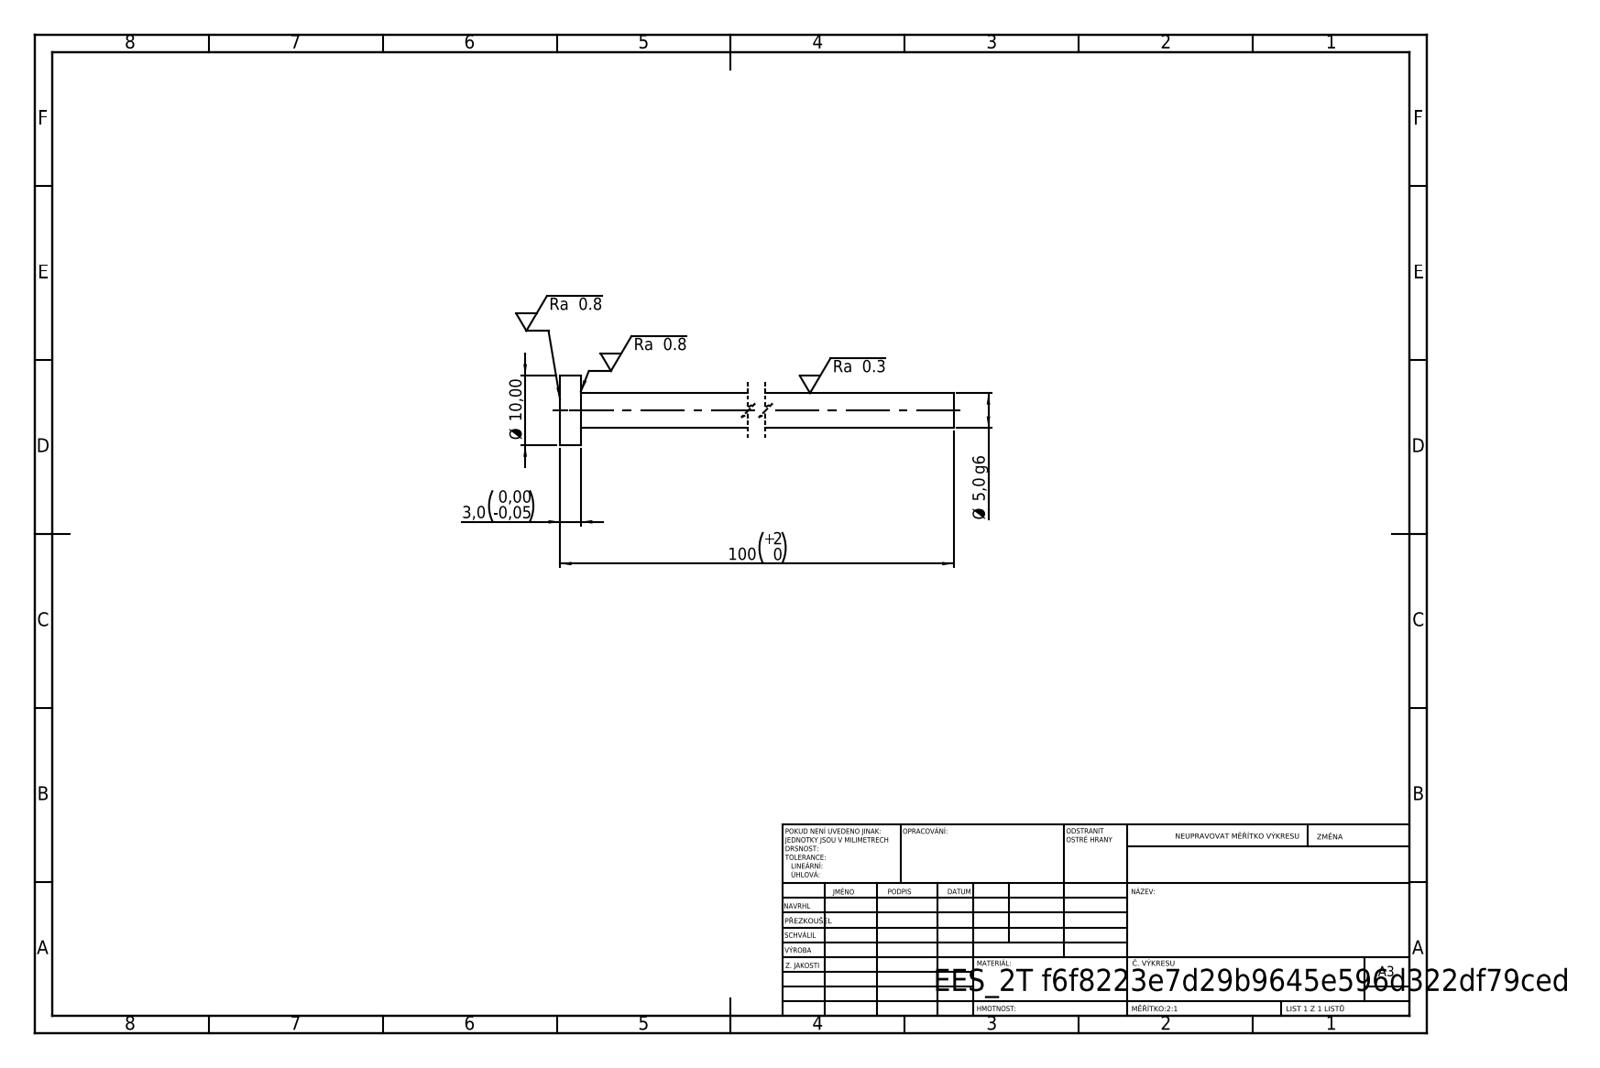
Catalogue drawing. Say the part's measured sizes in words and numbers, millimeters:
Its 3-D file was written by "SolidWorks 2019 (CONFIG_CONTROL_DESIGN)". It is 1 solid with 7 faces: 3 planar, 4 cylindrical and 0 other. Overall it measures 100 by 10 by 10 millimeters. Its volume is 2 140 cubic millimeters and its surface area 1 775 square millimeters. Round bosses or shafts: 1 of diameter 10, 1 of diameter 5. The main face-to-face distances are 3, 100, 97.
